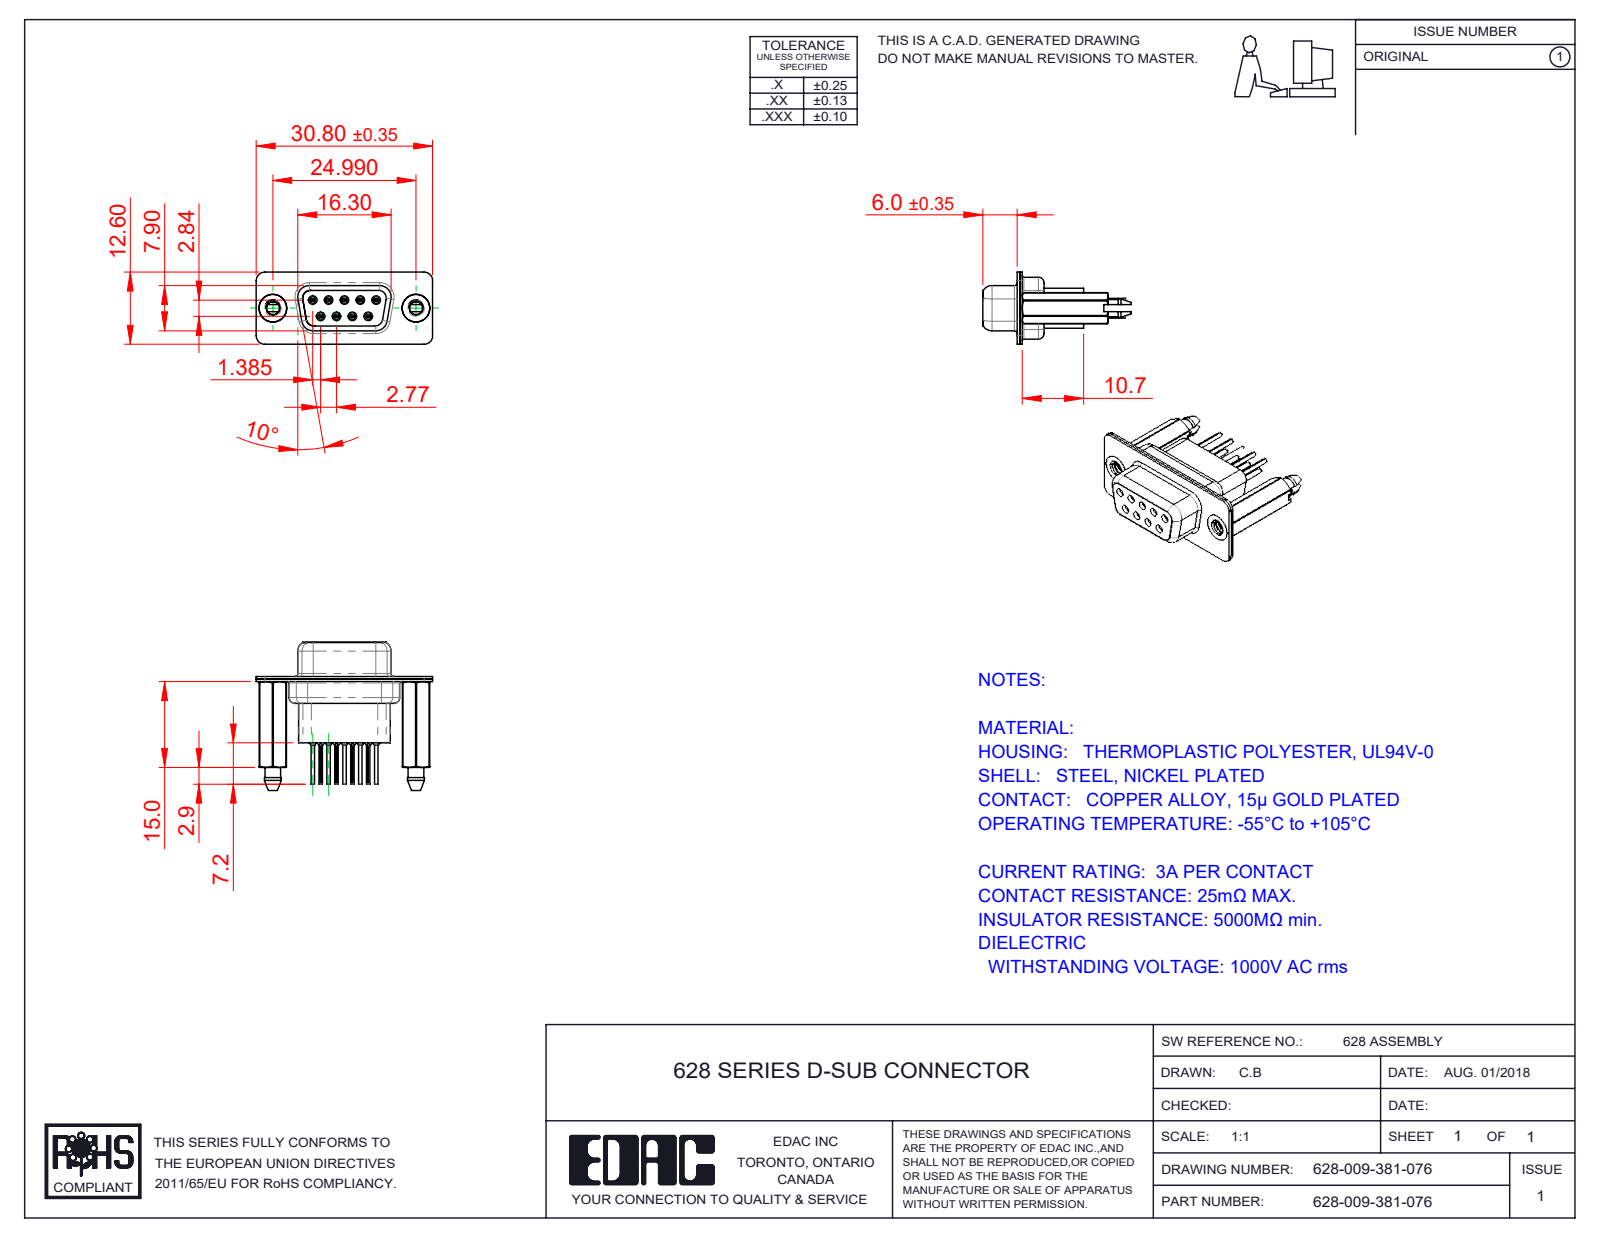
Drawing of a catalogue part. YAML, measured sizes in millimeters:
part_name: "628 Shell Rear_09 Contacts; 628 4-40 Threaded Boardlock_HP81; 628 Shell Front_09 Contacts; 628 Contact Row 1_71 (+3 more)"
step_written_by: "SolidWorks 2020 (CONFIG_CONTROL_DESIGN)"
units: millimeters
bodies: {solids: 14, faces: 1460, planar: 378, cylindrical: 466, other: 616}
overall_size: [30.8, 25.9, 12.6]
volume: 2635
surface_area: 6123
round_holes:
  - {diameter: 0.2, count: 9}
  - {diameter: 0.8, count: 9}
  - {diameter: 0.9, count: 9}
  - {diameter: 1.1, count: 9}
  - {diameter: 1.6, count: 9}
  - {diameter: 1.7, count: 5}
  - {diameter: 2.26, count: 2}
  - {diameter: 4, count: 2}
  - {diameter: 4.05, count: 2}
  - {diameter: 4.85, count: 2}
round_bosses_or_shafts:
  - {diameter: 2, count: 9}
  - {diameter: 1.5, count: 9}
  - {diameter: 1.2, count: 9}
  - {diameter: 0.6, count: 9}
  - {diameter: 4.95, count: 2}
  - {diameter: 4.8, count: 2}
partial_cylinders:
  - {radius: 1.5, count: 19}
  - {radius: 0.1, count: 18}
  - {radius: 2, count: 12}
  - {radius: 0.28, count: 9}
  - {radius: 1.35, count: 6}
  - {radius: 1.6, count: 6}
  - {radius: 0.25, count: 4}
  - {radius: 0.5, count: 4}
face_to_face_distances: [0.45, 0.4, 0.9, 8.5, 6.6, 4.76, 1.9, 1.4, 7, 10.7]
hole_center_spacings: [3.16, 2.77, 5.54, 5.03, 5.04, 8.31, 7.48, 7.49]
